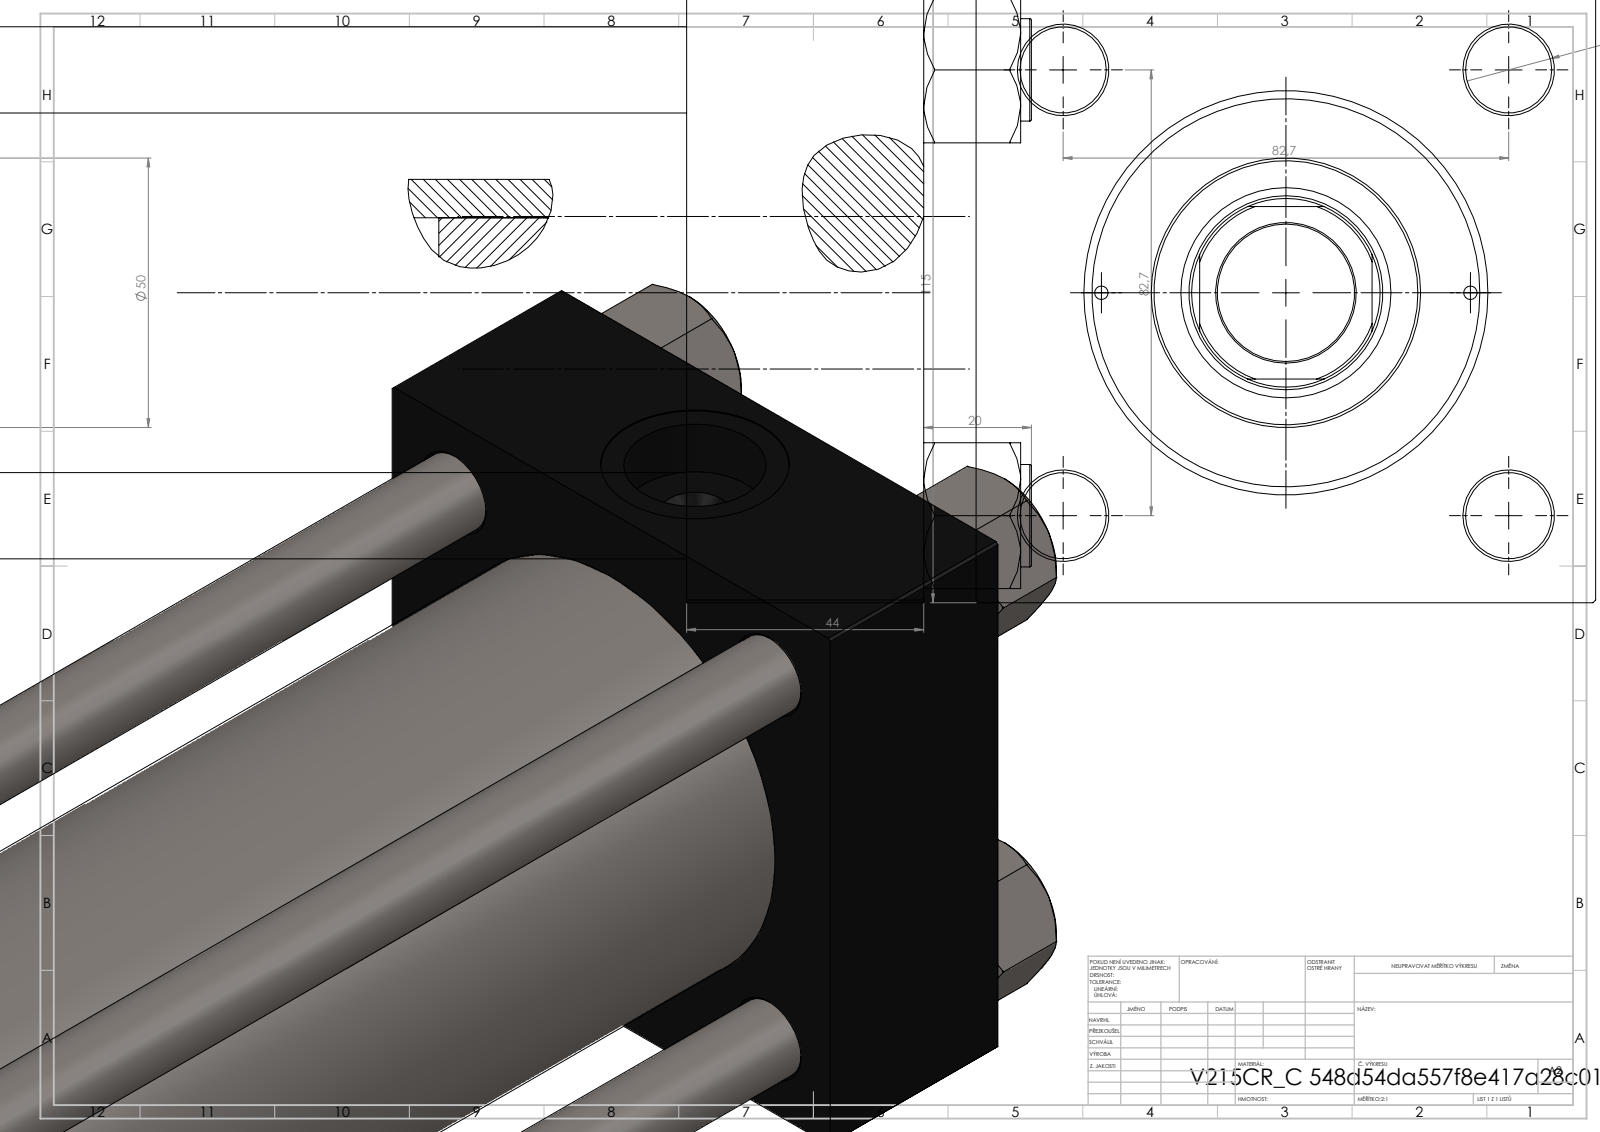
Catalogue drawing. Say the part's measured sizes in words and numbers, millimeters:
The part is named "V215CR_C_TYCINKA; V215CR_VCP_C; V215_VC_A; NUT_M5_C (+1 more)". Its 3-D file was written by "SolidWorks 2019 (CONFIG_CONTROL_DESIGN)". It is 11 solids with 1203 faces: 576 planar, 91 cylindrical and 536 other. Overall it measures 460 by 115 by 115 millimeters. Its volume is 2 385 000 cubic millimeters and its surface area 460 723 square millimeters. Round holes: 4 of diameter 16, 2 of diameter 2.5, 2 of diameter 7, 2 of diameter 26.44, 2 of diameter 35, 1 of diameter 25.5, 1 of diameter 36, 1 of diameter 39, 1 of diameter 61, 1 of diameter 72, 1 of diameter 80. Round bosses or shafts: 4 of diameter 19, 1 of diameter 86, 1 of diameter 50. Partial cylindrical surfaces (rounded edges, fillets, slot ends): 1 of radius 17.5. The main face-to-face distances are 115, 44, 409, 365, 69, 340, 296, 380.3, 336.3, 40.3. The hole center spacings are 41.96, 58.48, 82.7, 86.17, 34.25, 116.96, 68.5, 341.
